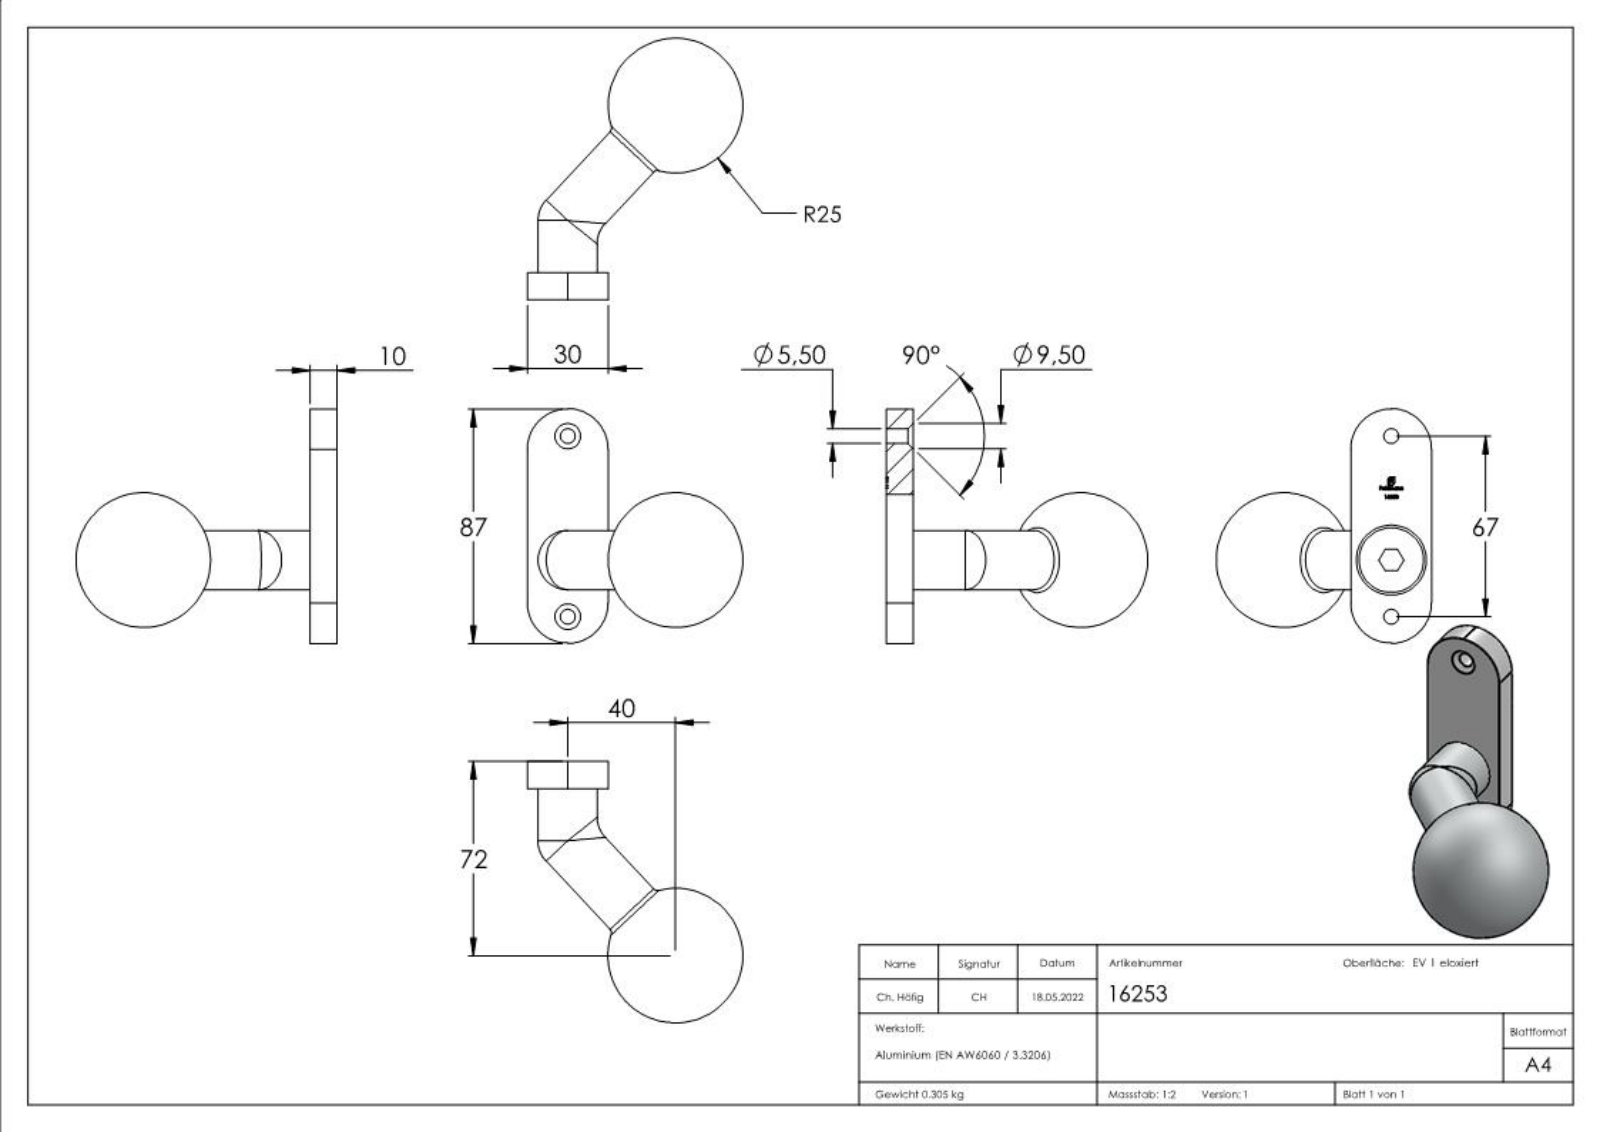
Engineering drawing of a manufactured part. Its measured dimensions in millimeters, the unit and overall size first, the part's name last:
Units: millimetres
Overall size (bounding box): 96 × 87 × 83
Round holes (diameter × count): ⌀5.5 ×2, ⌀10.2 ×1, ⌀18 ×1, ⌀20 ×1, ⌀26 ×1
Round bosses / shafts (diameter × count): ⌀22 ×2, ⌀24 ×1, ⌀23.5 ×1, ⌀19.75 ×1, ⌀12 ×1
Partial cylindrical surfaces — rounded edges, fillets, slot ends (radius × count): R0.75 ×2, R15 ×2
Main face-to-face distances: 10, 2, 3.5, 30, 8, 6.5, 4.5, 1, 6, 2.5
Hole centre spacings: 21, 46, 67
Volume: 107 286 mm³ · Surface area: 22 445 mm²
Bodies: 4 solids, 276 faces (141 planar, 19 cylindrical, 116 other)
Part name (STEP PRODUCT): DIN 7991 Konfig_M12x20; 16253 Teil1_16253 Teil1; 16253 Teil2_16253 Teil2; 16253 Teil3_15261 Teil3 (+1 more)
STEP written by: SolidWorks 2018 (CONFIG_CONTROL_DESIGN)
